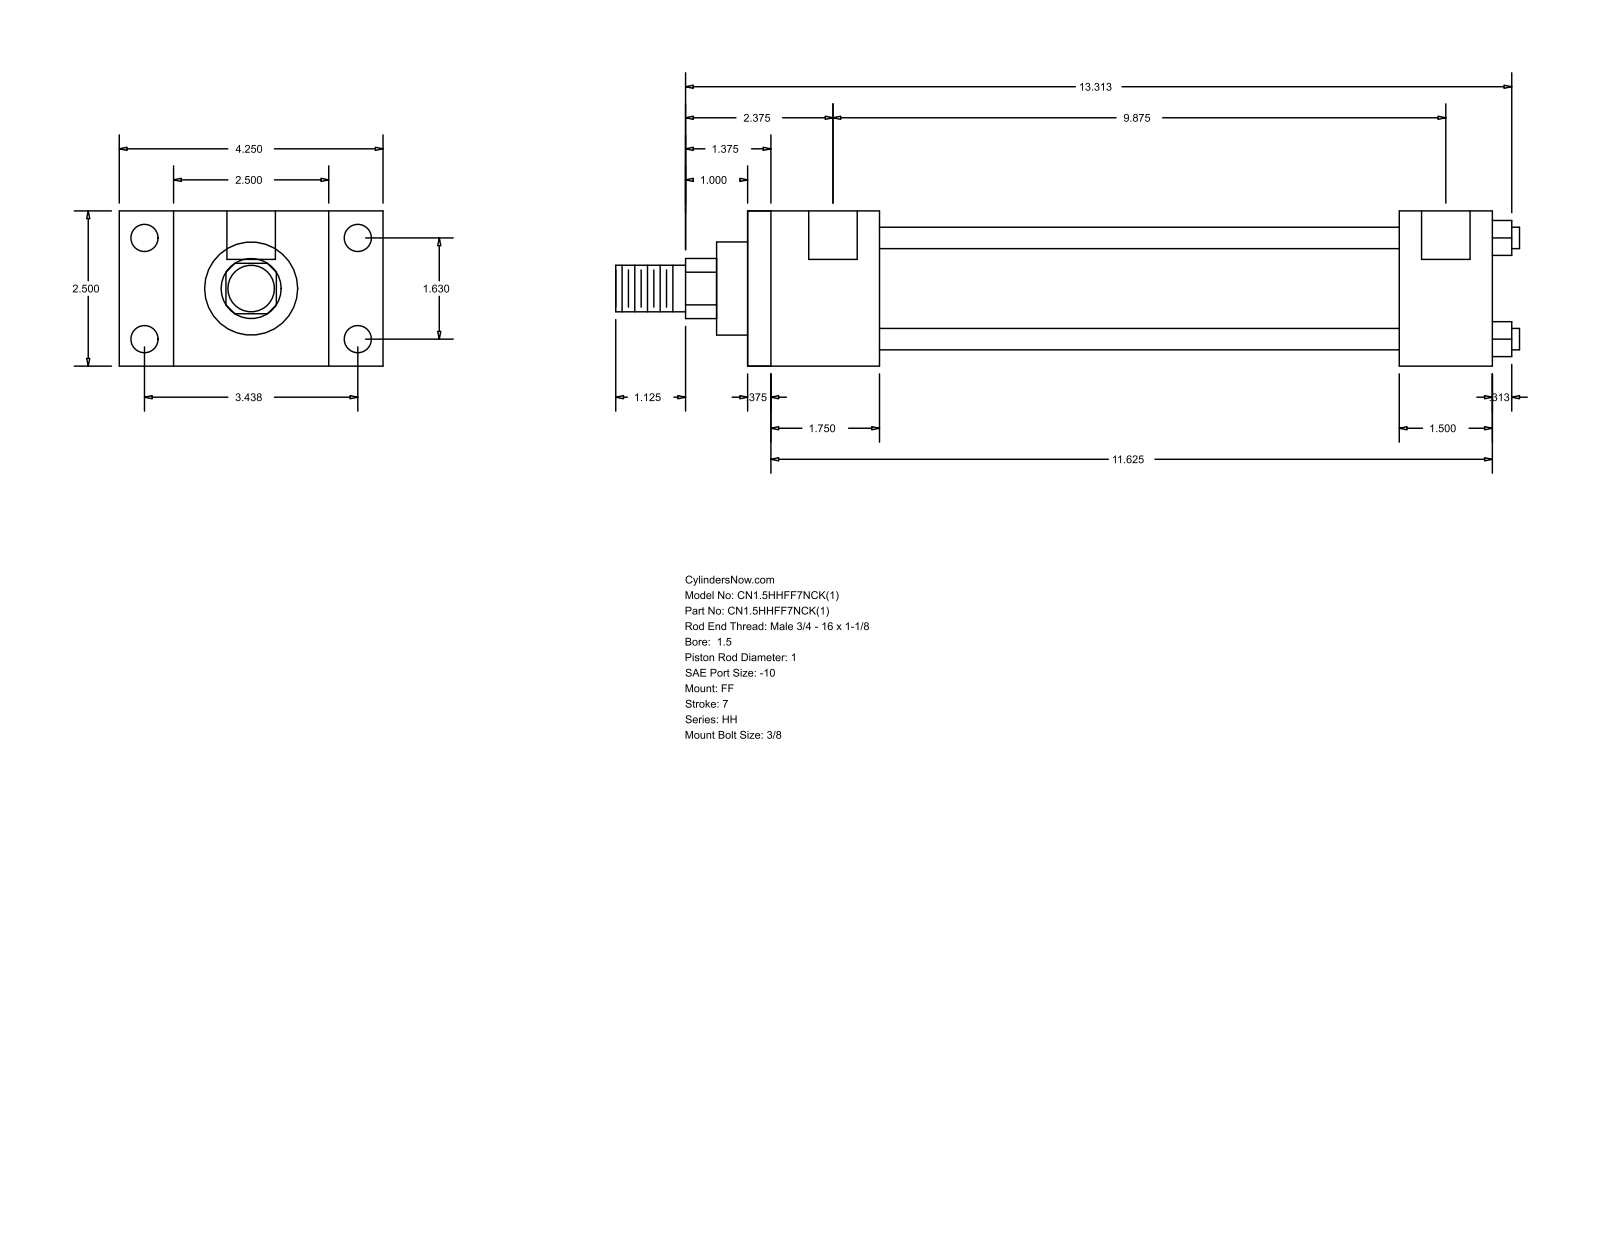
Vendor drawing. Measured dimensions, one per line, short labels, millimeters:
name: HH_FF__0150_1
written by: GSSL Pune (CONFIG_CONTROL_DESIGN)
unit: mm
bodies: 0 solids, 92 faces (64 planar, 28 cylindrical, 0 other)
size: 369.89 × 107.95 × 63.5
holes: 4× ⌀5.56, 4× ⌀11.13, 2× ⌀19.84
bosses: 4× ⌀8.76, 1× ⌀44.45, 1× ⌀38.1, 1× ⌀25.4, 1× ⌀19.05
rounds: 1× R12.29
face distances: 63.5, 304.8, 9.52, 295.28, 38.1, 53.98, 44.46, 250.82, 266.7, 257.18
hole spacings: 1.59, 41.4, 87.32, 96.64, 252.41, 254, 250.82
